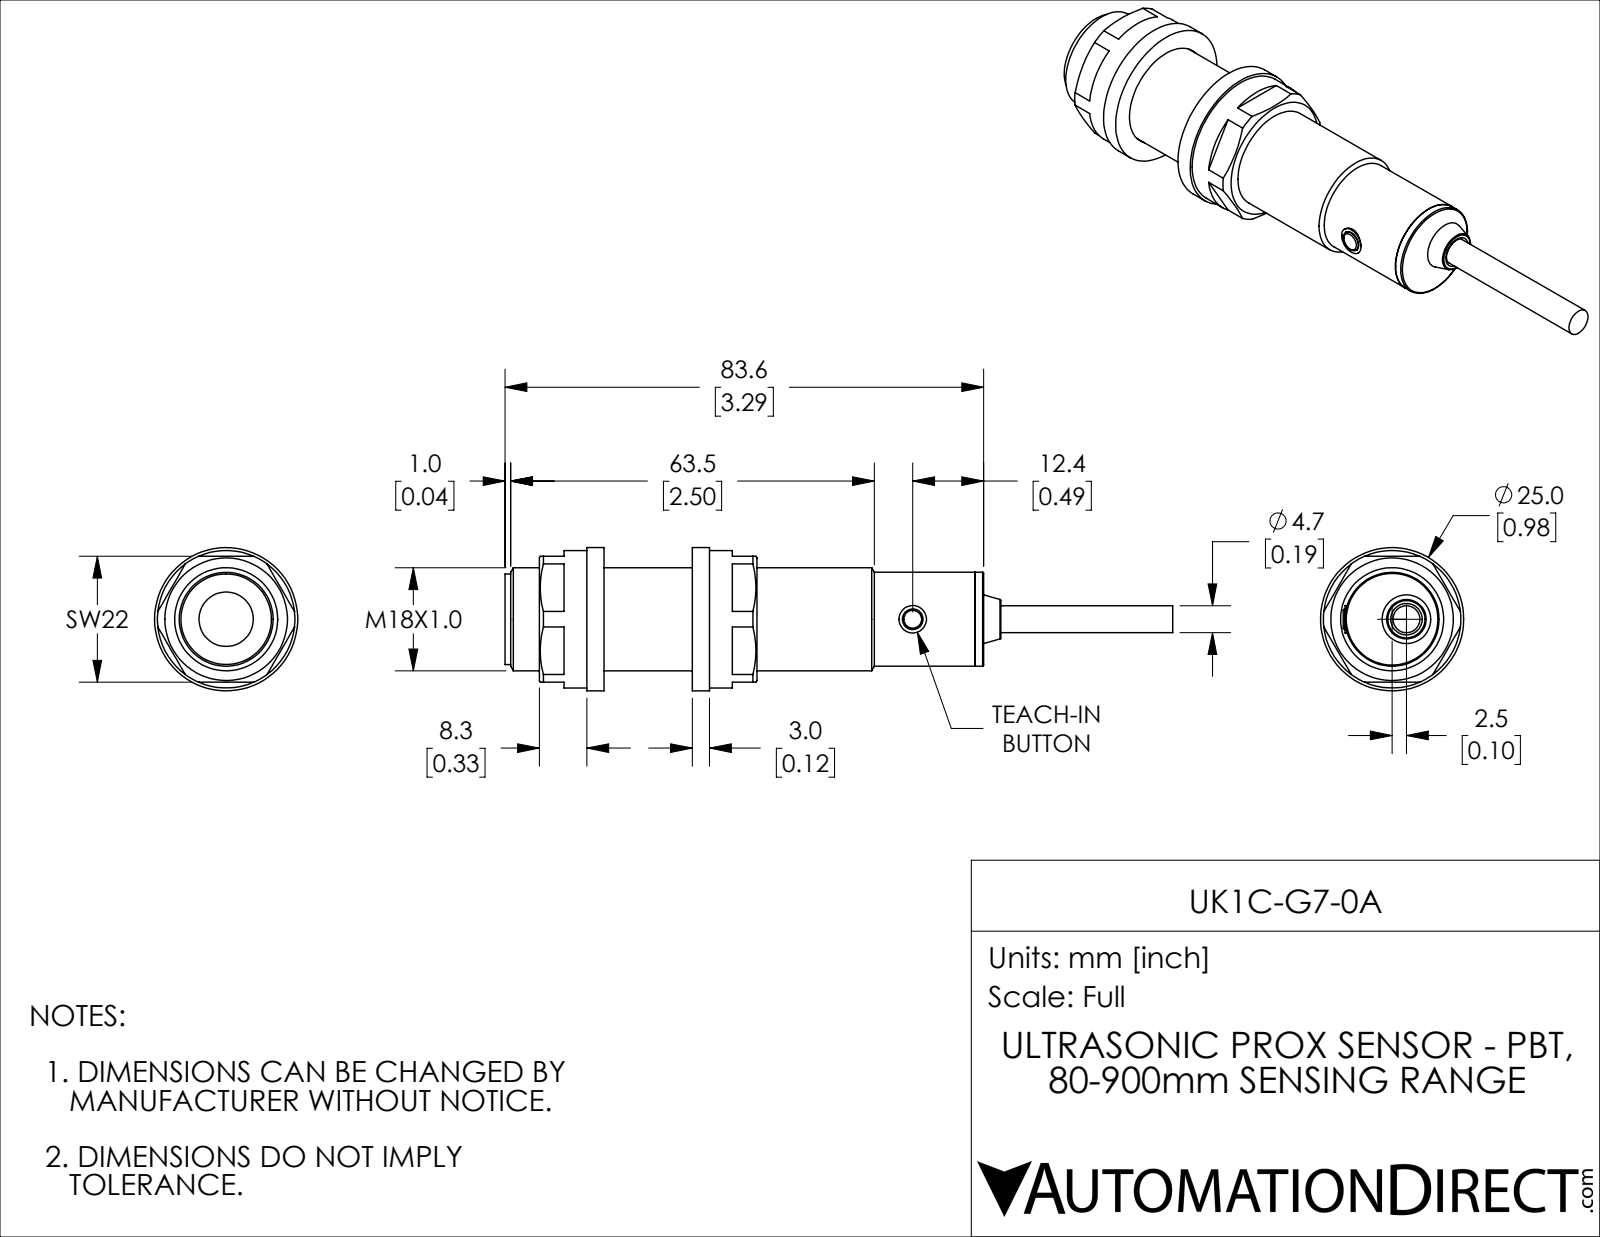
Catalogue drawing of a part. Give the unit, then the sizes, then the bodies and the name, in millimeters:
Units: millimetres
Overall size (bounding box): 116.6 × 25 × 25
Round holes (diameter × count): ⌀4.7 ×2, ⌀3.6 ×1, ⌀9.5 ×1, ⌀18 ×1, ⌀18.2 ×1
Round bosses / shafts (diameter × count): ⌀25 ×1, ⌀24 ×1, ⌀16.4 ×1, ⌀15.8 ×1, ⌀5.4 ×1, ⌀4.8 ×1
Main face-to-face distances: 3, 18.4, 21.4, 67.8, 46.4, 13.3, 34.7, 81.1, 16.3, 64.8
Hole centre spacings: 2.5
Volume: 25 220 mm³ · Surface area: 11 419 mm²
Bodies: 10 solids, 107 faces (49 planar, 40 cylindrical, 18 other)
Part name (STEP PRODUCT): UK1C-G7-0A
STEP written by: SolidWorks 2018 (AUTOMOTIVE_DESIGN)
